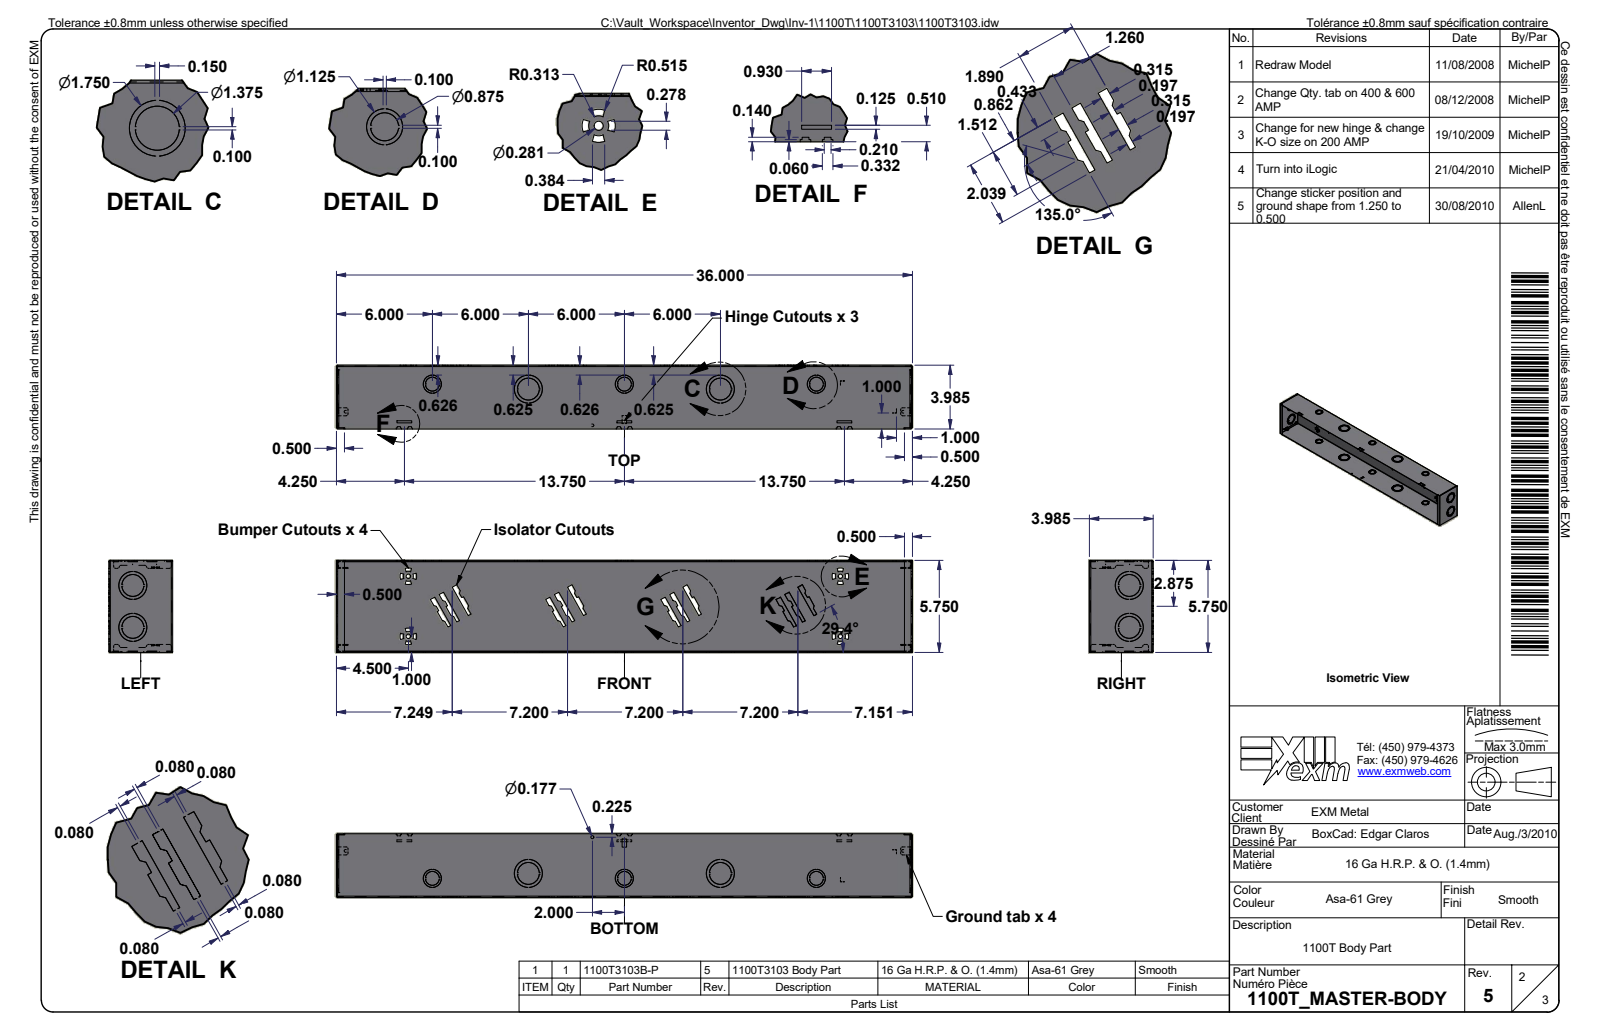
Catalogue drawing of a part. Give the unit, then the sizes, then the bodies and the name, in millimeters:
Units: millimetres
Overall size (bounding box): 914.4 × 160.2 × 123.7
Round holes (diameter × count): ⌀5.5 ×18, ⌀6 ×6, ⌀5.2 ×5, ⌀7.1 ×4, ⌀7.9 ×4, ⌀34.9 ×4, ⌀44.5 ×4, ⌀2 ×3, ⌀4.5 ×3, ⌀8.6 ×3, ⌀22.2 ×3, ⌀28.6 ×3
Round bosses / shafts (diameter × count): ⌀7.1 ×18, ⌀6.2 ×18, ⌀44.5 ×4, ⌀34.9 ×4, ⌀25.1 ×4, ⌀28.6 ×3, ⌀22.2 ×3, ⌀9.4 ×3
Partial cylindrical surfaces — rounded edges, fillets, slot ends (radius × count): R0.5 ×590, R0.3 ×432, R0.3 ×243, R1 ×239, R0.8 ×98, R2 ×87, R1.6 ×33, R5 ×32
Main face-to-face distances: 1.4, 144.7, 1.4, 101.2, 99.8, 101.2, 102.6, 143.3, 146.1, 913
Hole centre spacings: 182.9, 178.1, 34.9, 173.8, 188.1, 10.2, 10.2, 12.5
Volume: 865 700 mm³ · Surface area: 1 168 000 mm²
Bodies: 42 solids, 10307 faces (3774 planar, 3360 cylindrical, 3173 other)
Part name (STEP PRODUCT): 1100T3103; 1100T3103B; 1100T3103B-P; STK-A-881BRC125-1 (+8 more)
STEP written by: Autodesk Inventor 2024 (AUTOMOTIVE_DESIGN)
